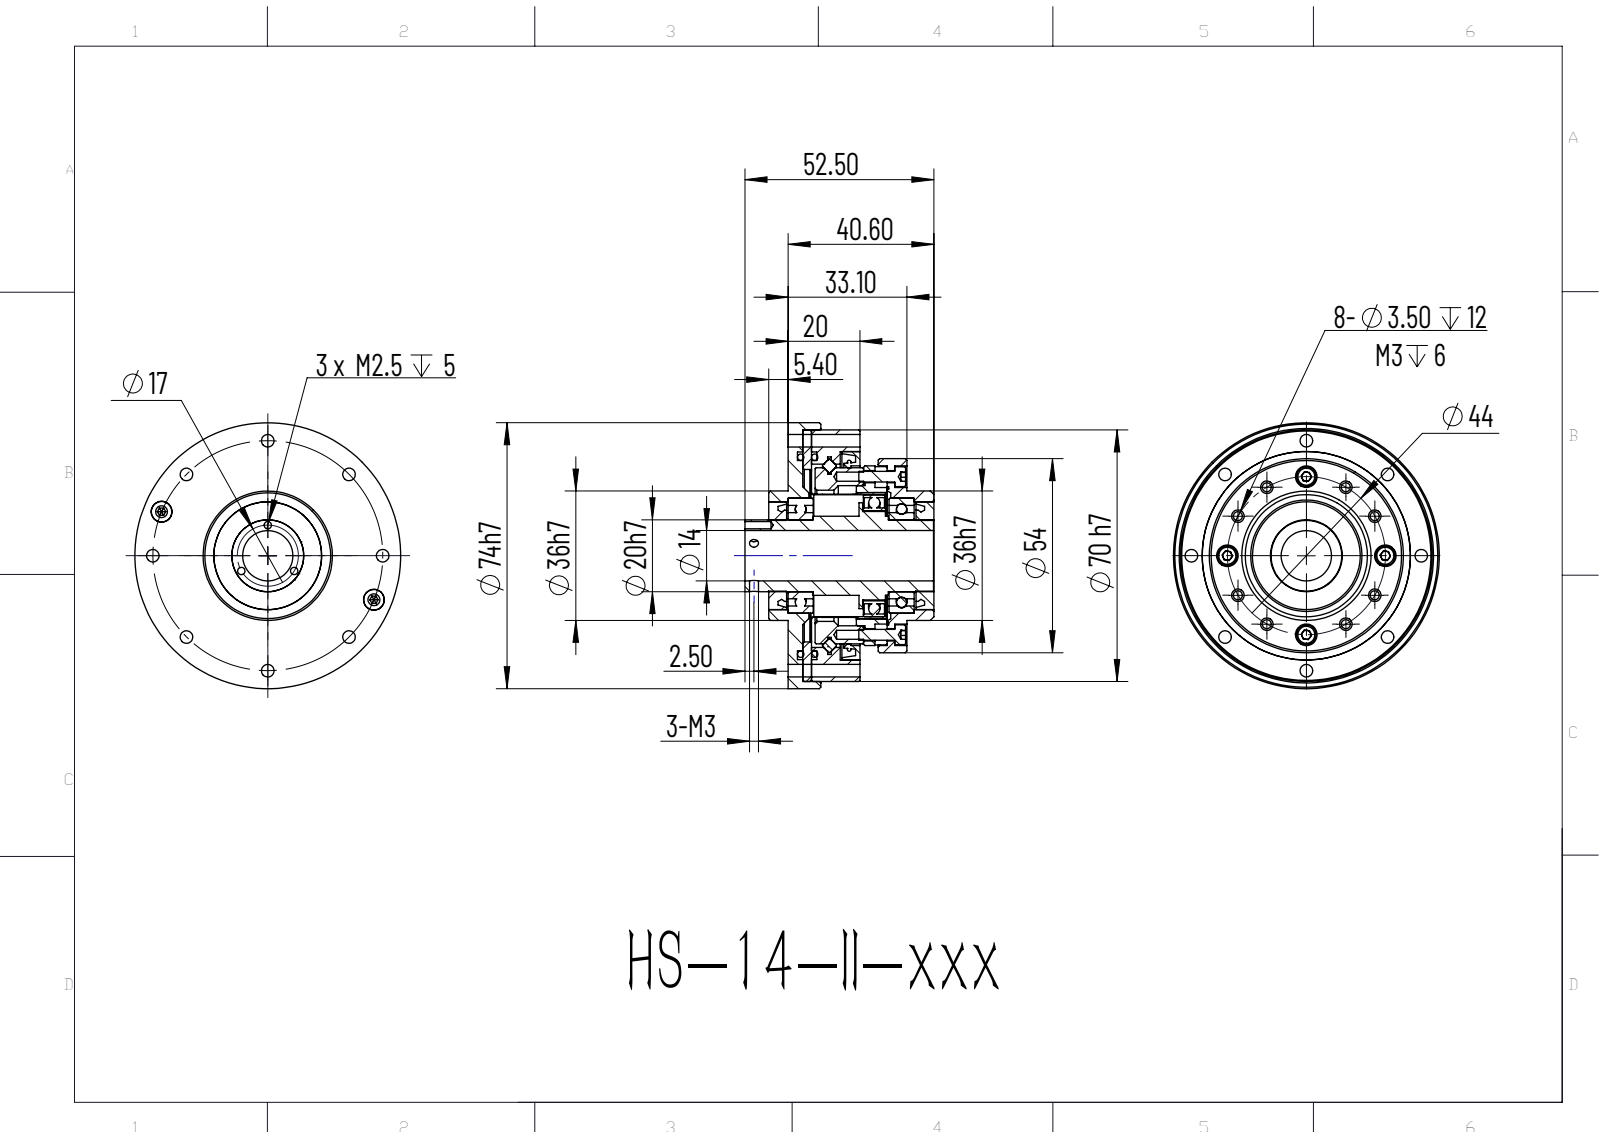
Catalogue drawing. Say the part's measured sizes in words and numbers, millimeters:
The part is named "HS-14-II; ??20X30X5; ??2; hexagon socket head cap screws gb_GB_FASTENER_SCREWS_HSHCS M3X10-C (+8 more)". Its 3-D file was written by "ONSHAPE BY PTC INC, 1.201 (AP242_MANAGED_MODEL_BASED_3D_ENGINEERING_MIM_LF)". It is 103 solids with 1113 faces: 462 planar, 297 cylindrical and 354 other. Overall it measures 74 by 74 by 52.6 millimeters. Its volume is 91 556 cubic millimeters and its surface area 83 789 square millimeters. Round holes: 18 of diameter 3.5, 17 of diameter 2.5, 6 of diameter 3.4, 6 of diameter 6, 3 of diameter 2.05, 1 of diameter 1.6, 1 of diameter 2.4, 1 of diameter 4.2, 1 of diameter 14, 1 of diameter 20, 1 of diameter 25.07, 1 of diameter 28. Round bosses or shafts: 47 of diameter 3, 4 of diameter 5.5, 1 of diameter 74, 1 of diameter 70, 1 of diameter 54, 1 of diameter 53, 1 of diameter 49, 1 of diameter 45.4. Partial cylindrical surfaces (rounded edges, fillets, slot ends): 40 of radius 1.52. The main face-to-face distances are 6.5, 4.1, 2.4, 13.5, 1, 7.5, 5.5, 14.5, 27.6, 20. The hole center spacings are 22, 31.11, 38.1, 42.5, 11.39, 12.17, 16.99, 22.64.
